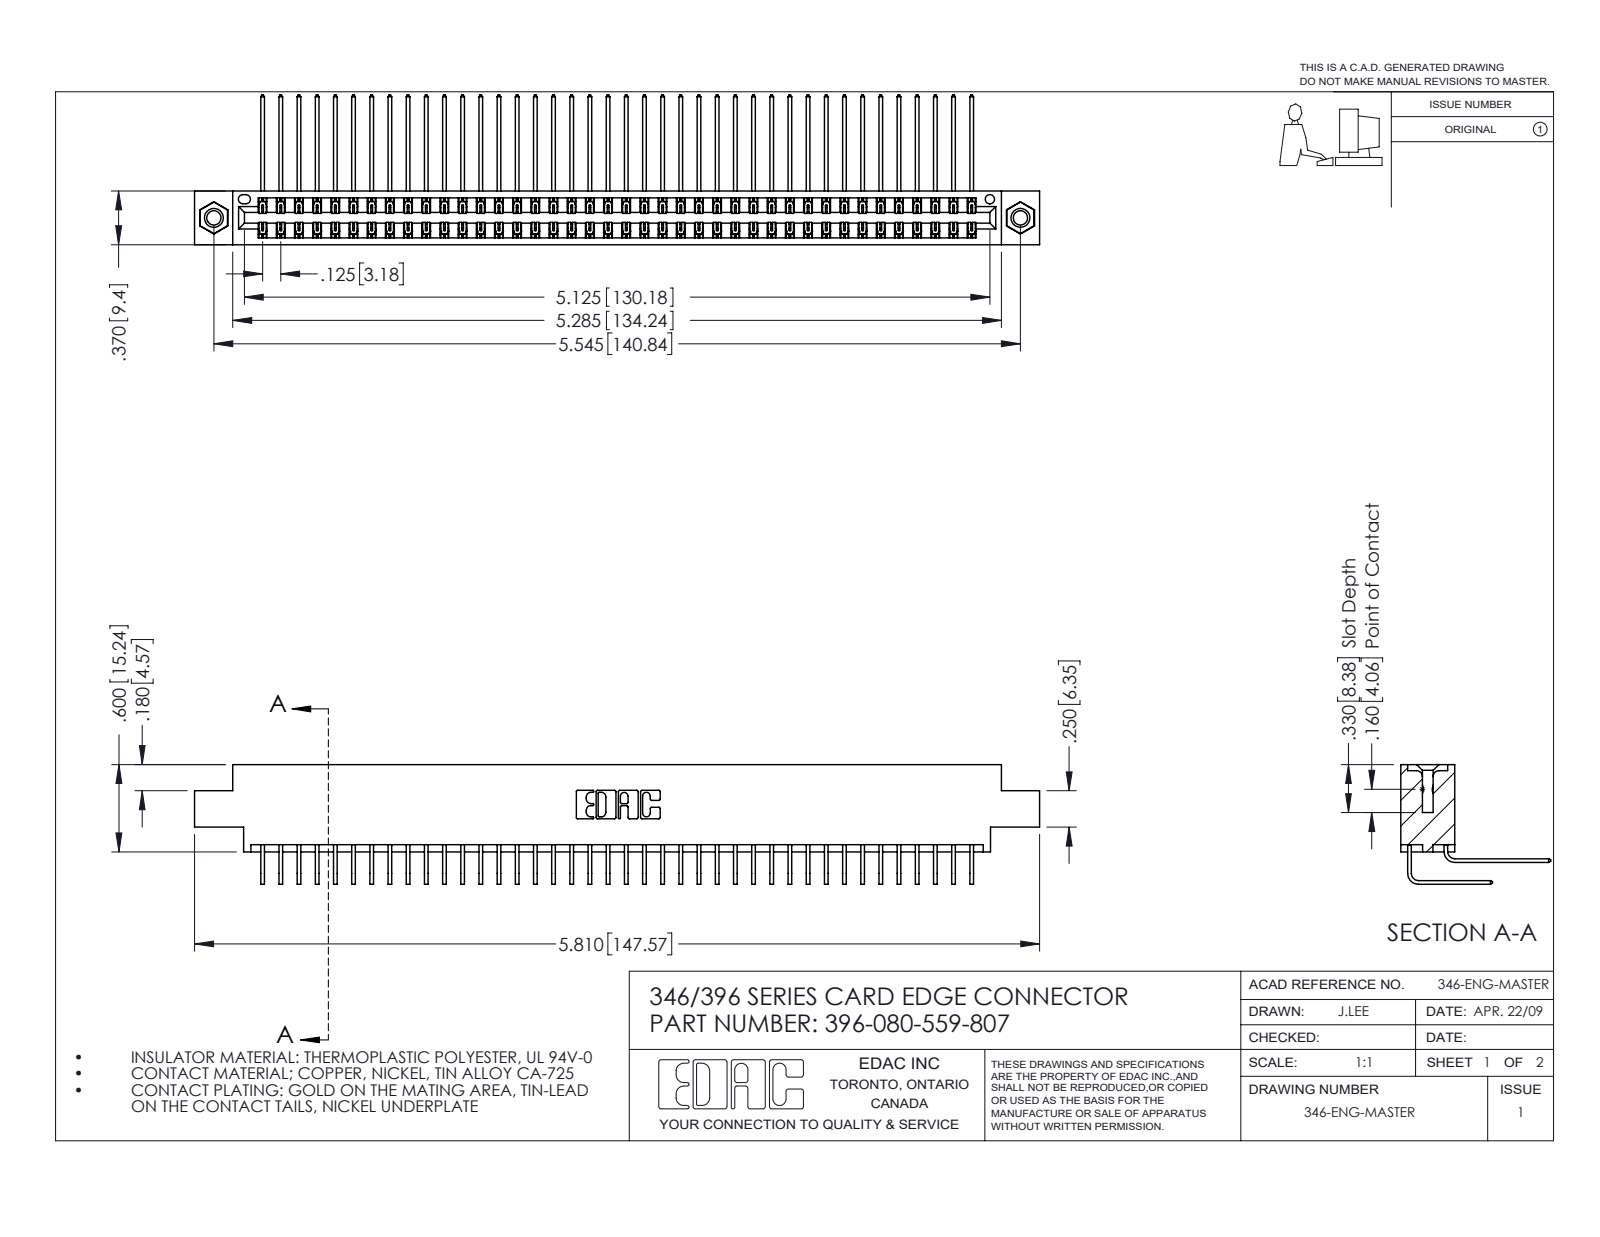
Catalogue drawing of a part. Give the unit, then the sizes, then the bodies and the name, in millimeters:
Units: millimetres
Overall size (bounding box): 147.6 × 26.2 × 20.9
Round holes (diameter × count): ⌀2.5 ×2, ⌀3.2 ×2, ⌀4 ×2, ⌀1.6 ×1
Round bosses / shafts (diameter × count): ⌀3.9 ×2
Partial cylindrical surfaces — rounded edges, fillets, slot ends (radius × count): R0.2 ×120, R0.3 ×22, R0.2 ×6, R0.8 ×6, R0.7 ×3, R0.4 ×2, R0.6 ×2, R0.6 ×2
Main face-to-face distances: 1.2, 8.2, 0.6, 9.4, 6.4, 1.8, 7.6, 7, 5.6, 3.8
Hole centre spacings: 6.2, 135.5, 140.8
Volume: 14 700 mm³ · Surface area: 22 560 mm²
Bodies: 83 solids, 4506 faces (3072 planar, 1418 cylindrical, 16 other)
Part name (STEP PRODUCT): 396-080-559-807; 345-292-001_559 Tail - 2; 345-292-001_558 559 Tail - 1; 346 Part_0.170 Offset - 0.156 Dia-TI (+1 more)
STEP written by: SolidWorks 2016 (CONFIG_CONTROL_DESIGN)
